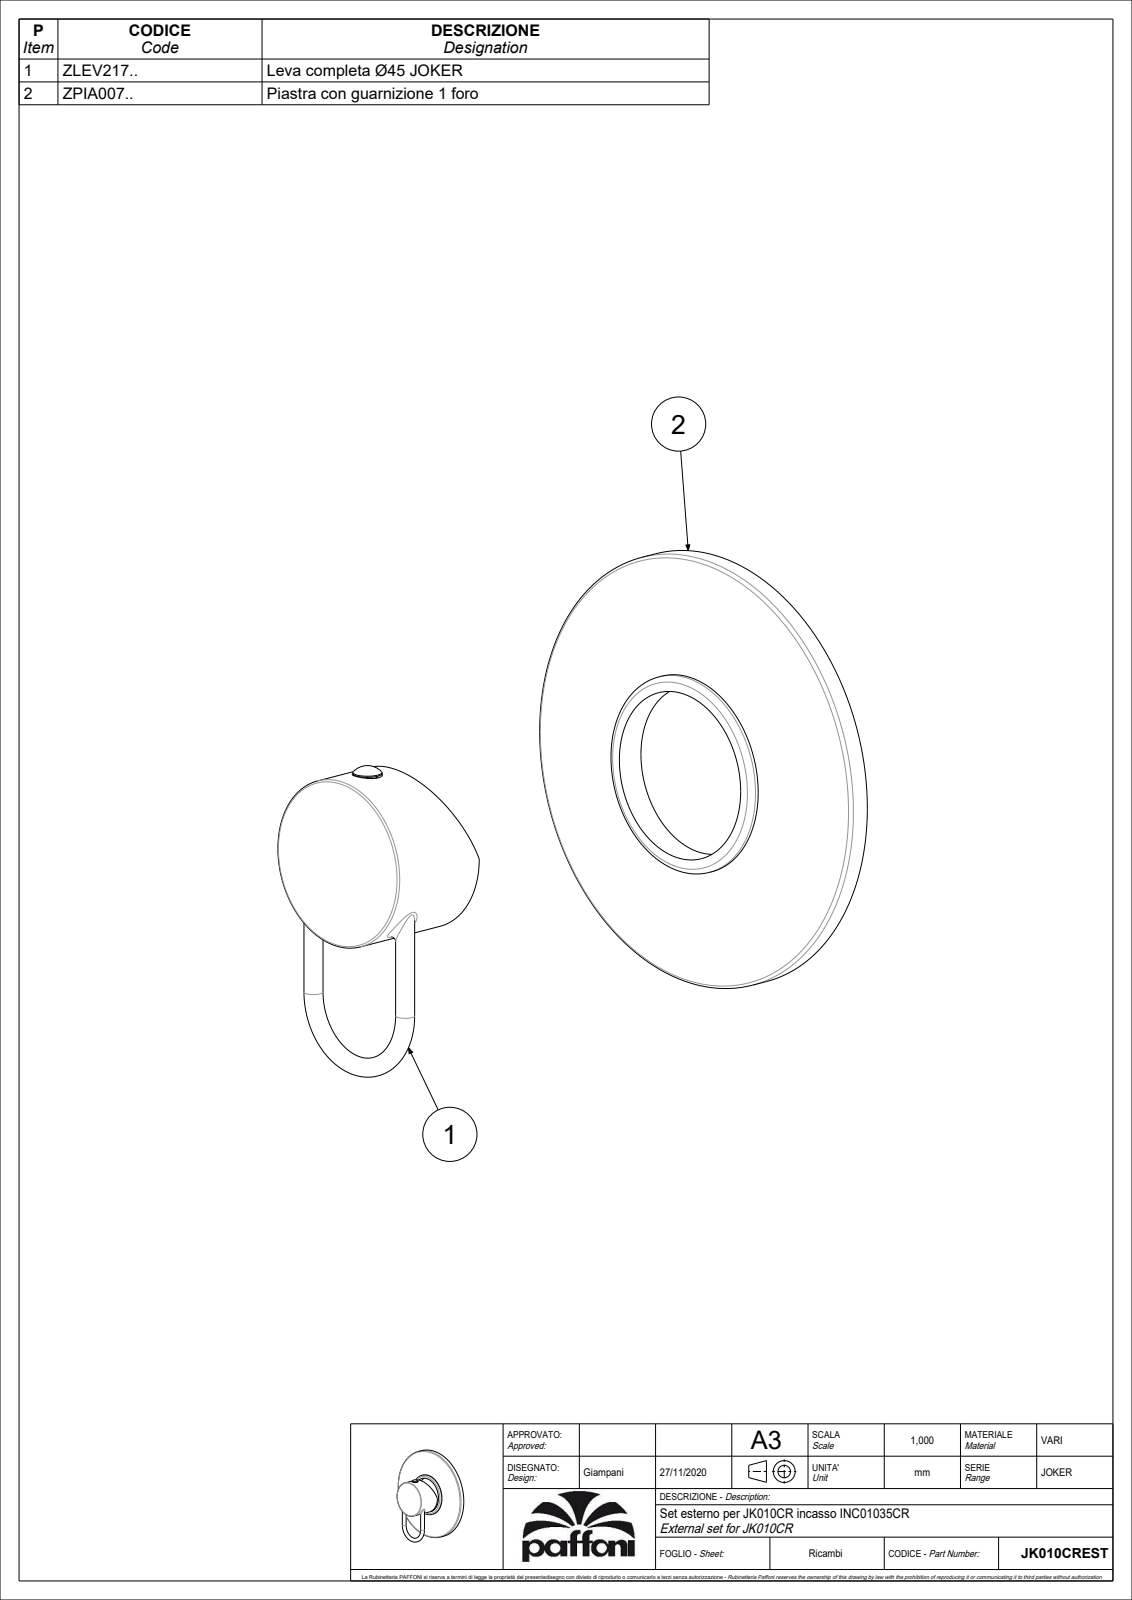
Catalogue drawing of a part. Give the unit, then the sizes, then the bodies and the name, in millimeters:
Units: millimetres
Overall size (bounding box): 117 × 116 × 43.89
Round holes (diameter × count): ⌀3 ×1, ⌀8 ×1, ⌀45 ×1, ⌀50 ×1, ⌀114 ×1
Round bosses / shafts (diameter × count): ⌀5 ×3, ⌀116 ×1, ⌀53 ×1, ⌀7.6 ×1, ⌀5.5 ×1
Partial cylindrical surfaces — rounded edges, fillets, slot ends (radius × count): R1.55 ×2
Main face-to-face distances: 4, 28, 11.5, 39.5, 2.5, 8, 7.5, 1.5, 3.5, 36
Volume: 26 373 mm³ · Surface area: 37 932 mm²
Bodies: 2 solids, 134 faces (45 planar, 46 cylindrical, 43 other)
Part name (STEP PRODUCT): JK010CREST
STEP written by: CREO PARAMETRIC BY PTC INC, 2020044 (CONFIG_CONTROL_DESIGN)
